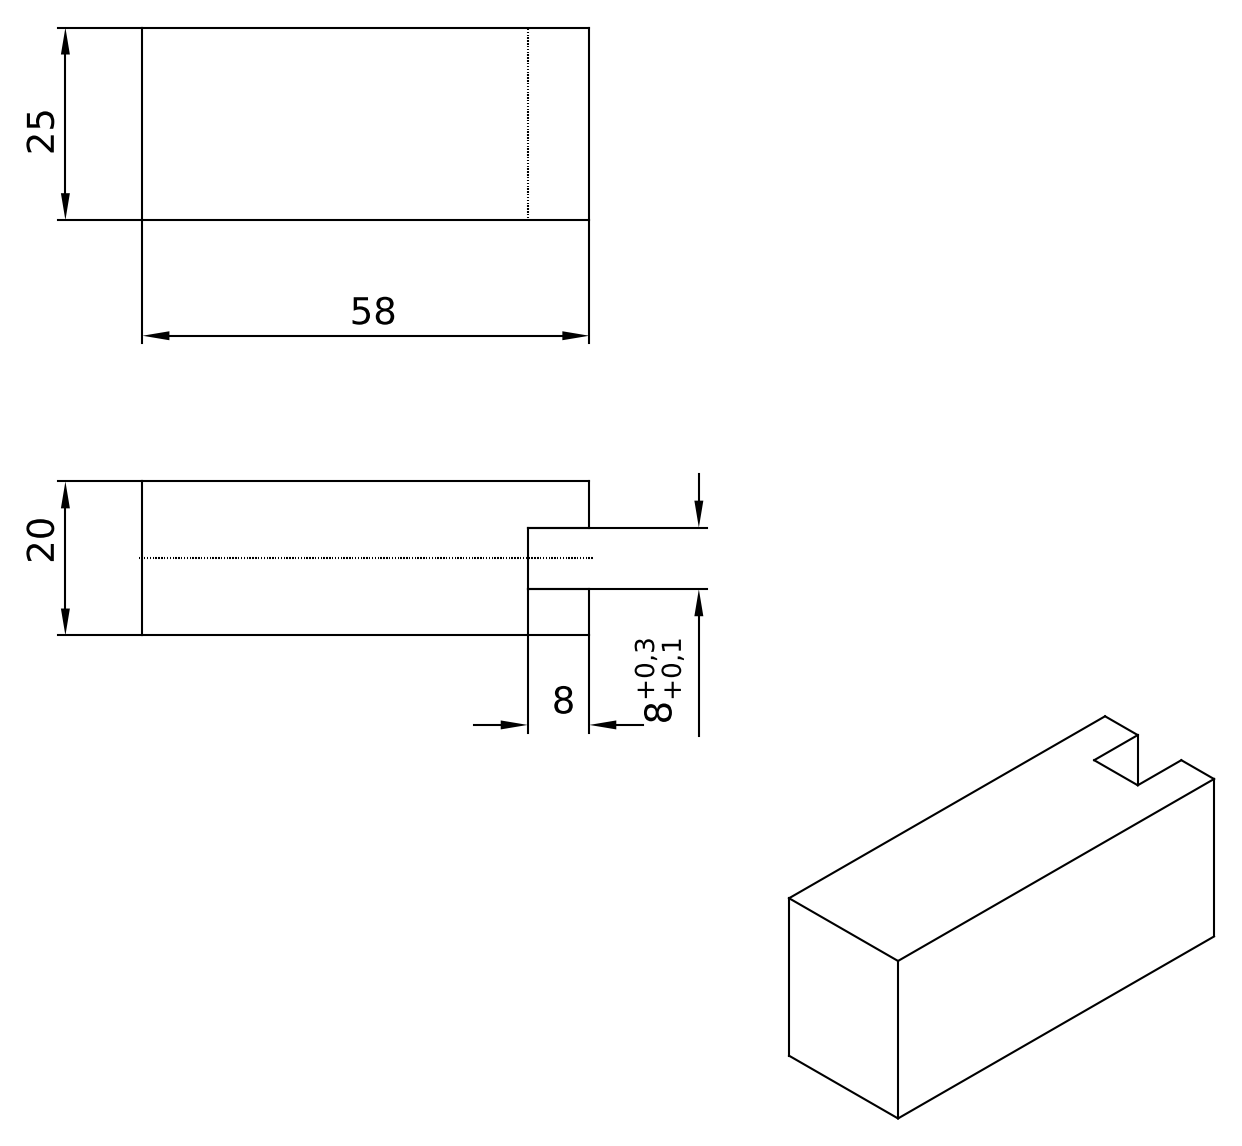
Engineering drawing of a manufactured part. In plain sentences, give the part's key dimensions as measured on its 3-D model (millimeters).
The part is named "603-21E1". Its 3-D file was written by "Autodesk Inventor 8 (AUTOMOTIVE_DESIGN)". It is 1 solid with 10 faces: 10 planar, 0 cylindrical and 0 other. Overall it measures 58 by 25 by 20 millimeters. Its volume is 27 400 cubic millimeters and its surface area 6 492 square millimeters. The main face-to-face distances are 20, 25, 6, 14, 8, 58, 50.
